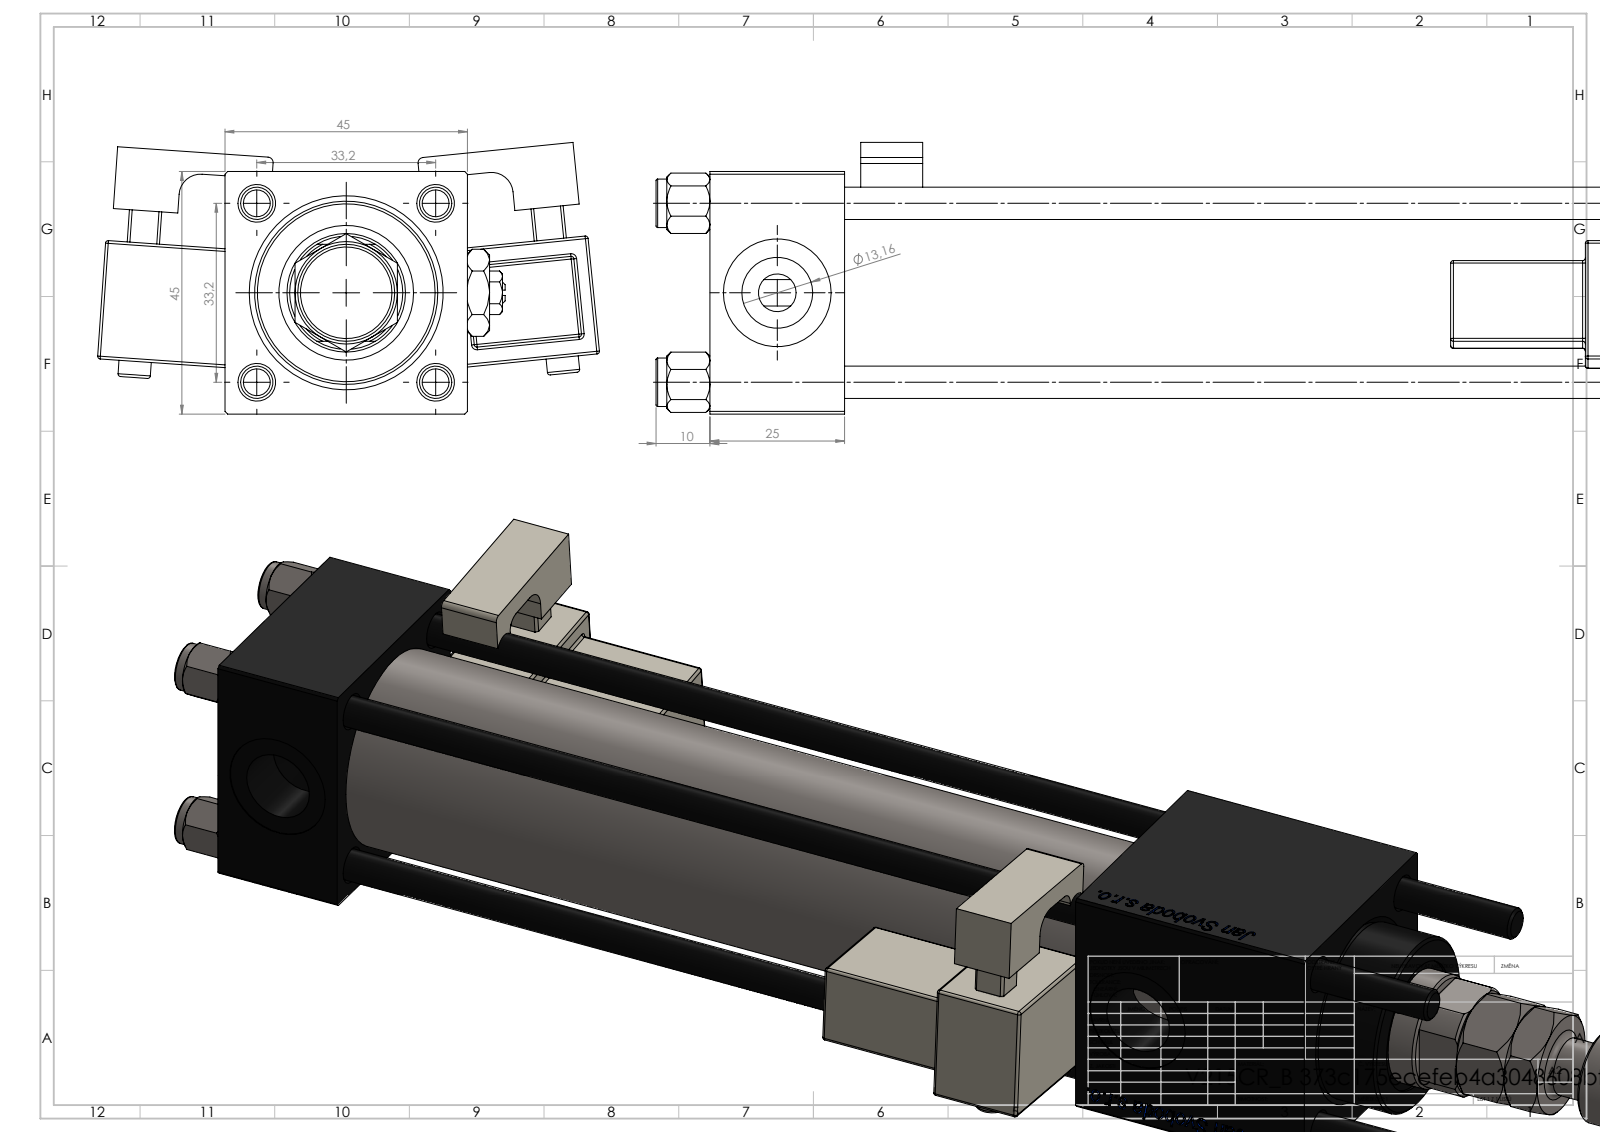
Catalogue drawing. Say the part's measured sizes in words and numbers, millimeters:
The part is named "V215CR_B-1; V215CR_VCP_B; NUT_M5_B; V215CR_B_TYCINKA (+4 more)". Its 3-D file was written by "SolidWorks 2019 (CONFIG_CONTROL_DESIGN)". It is 16 solids with 1466 faces: 556 planar, 152 cylindrical and 758 other. Overall it measures 296 by 93.14 by 50.4 millimeters. Its volume is 347 931 cubic millimeters and its surface area 131 592 square millimeters. Round holes: 4 of diameter 6, 2 of diameter 7, 2 of diameter 13.16, 2 of diameter 20, 1 of diameter 10.5, 1 of diameter 22, 1 of diameter 24, 1 of diameter 25, 1 of diameter 32, 1 of diameter 33. Round bosses or shafts: 4 of diameter 9, 2 of diameter 6, 1 of diameter 38, 1 of diameter 34, 1 of diameter 18, 1 of diameter 11. Partial cylindrical surfaces (rounded edges, fillets, slot ends): 48 of radius 0.5, 2 of radius 1, 2 of radius 2.5, 2 of radius 4, 1 of radius 10.5. The main face-to-face distances are 45, 25, 180, 155, 228, 3, 137.5, 17.5, 44.8, 39.5. The hole center spacings are 23.48, 33.2, 46.95, 180.5.
